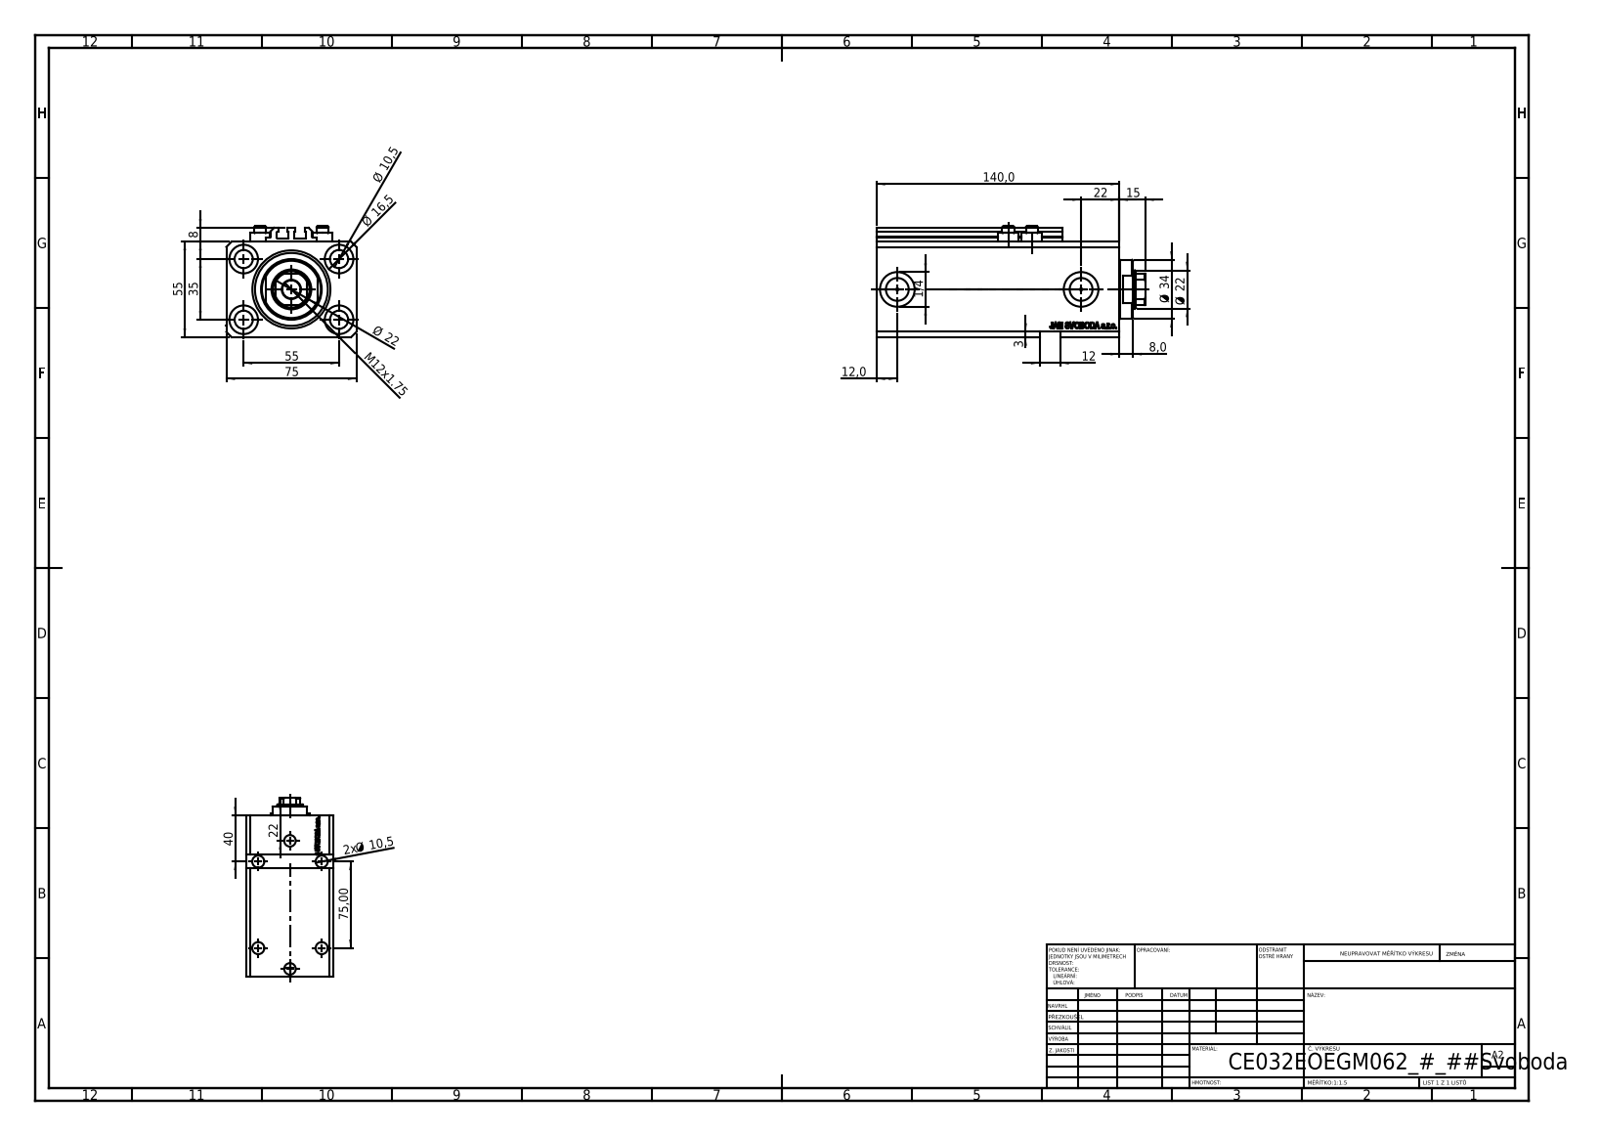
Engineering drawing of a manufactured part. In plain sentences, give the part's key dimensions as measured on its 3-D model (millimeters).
The part is named "V250CE_E_Body; ALLEN BOLT V250CE; V250CE_C_VCP; V250CE_VC_E". Its 3-D file was written by "SolidWorks 2019 (CONFIG_CONTROL_DESIGN)". It is 8 solids with 1084 faces: 514 planar, 146 cylindrical and 424 other. Overall it measures 155 by 75 by 64 millimeters. Its volume is 485 219 cubic millimeters and its surface area 115 303 square millimeters. Round holes: 9 of diameter 10.5, 4 of diameter 1.25, 4 of diameter 4, 4 of diameter 16.5, 2 of diameter 10, 2 of diameter 13.16, 2 of diameter 20, 1 of diameter 22, 1 of diameter 32, 1 of diameter 45. Round bosses or shafts: 4 of diameter 11.6, 4 of diameter 7, 1 of diameter 34. Partial cylindrical surfaces (rounded edges, fillets, slot ends): 10 of radius 0.2, 1 of radius 10.5. The main face-to-face distances are 55, 75, 15, 140, 125, 3, 9.9, 57, 115.1, 130.1. The hole center spacings are 32.6, 32.87, 55, 96.98, 13.6, 14.09, 25.81, 32.58.
